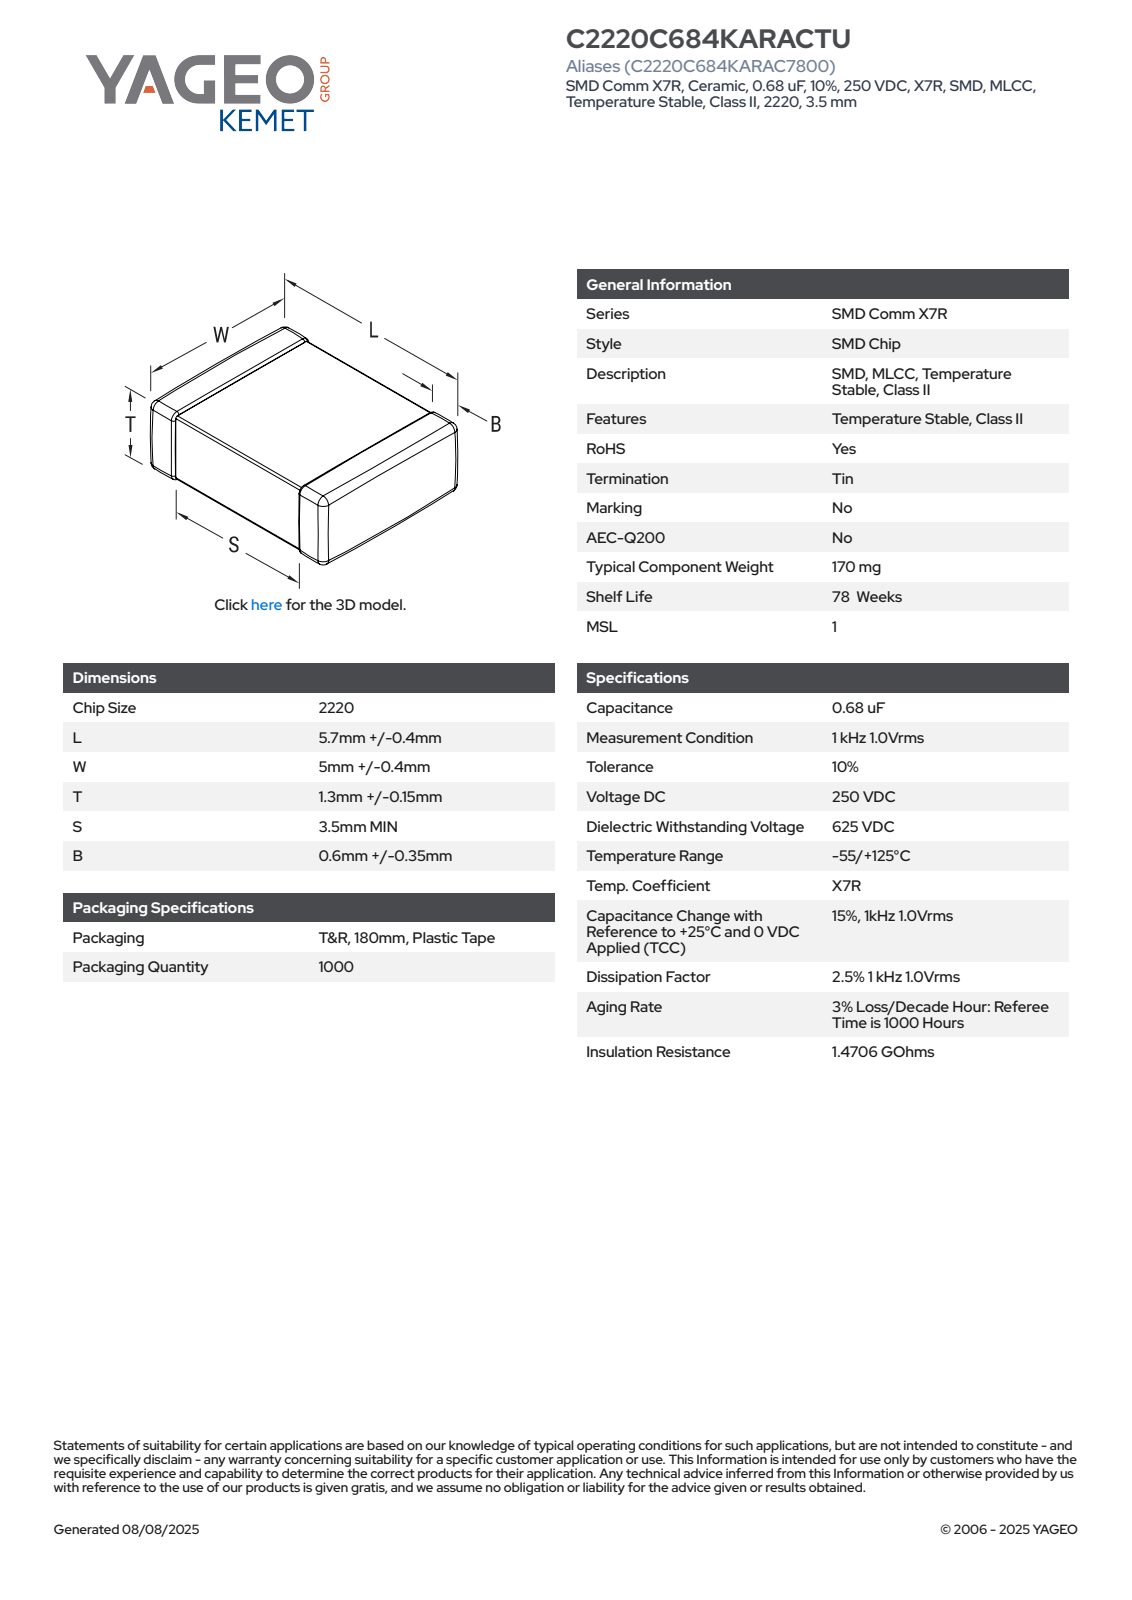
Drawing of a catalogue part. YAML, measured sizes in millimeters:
part_name: "CCS_CCSTD_2220_L6.1W5.4T1.45B0.6"
step_written_by: "SolidWorks 2021 (AUTOMOTIVE_DESIGN)"
units: millimeters
bodies: {solids: 4, faces: 125, planar: 71, cylindrical: 38, other: 16}
overall_size: [6.1, 5.4, 1.45]
volume: 41
surface_area: 98
partial_cylinders:
  - {radius: 0.11, count: 24}
face_to_face_distances: [1.23, 1.34, 1.45, 6.1, 5.18, 5.29, 5.4, 2.5, 3.6, 3.29]
